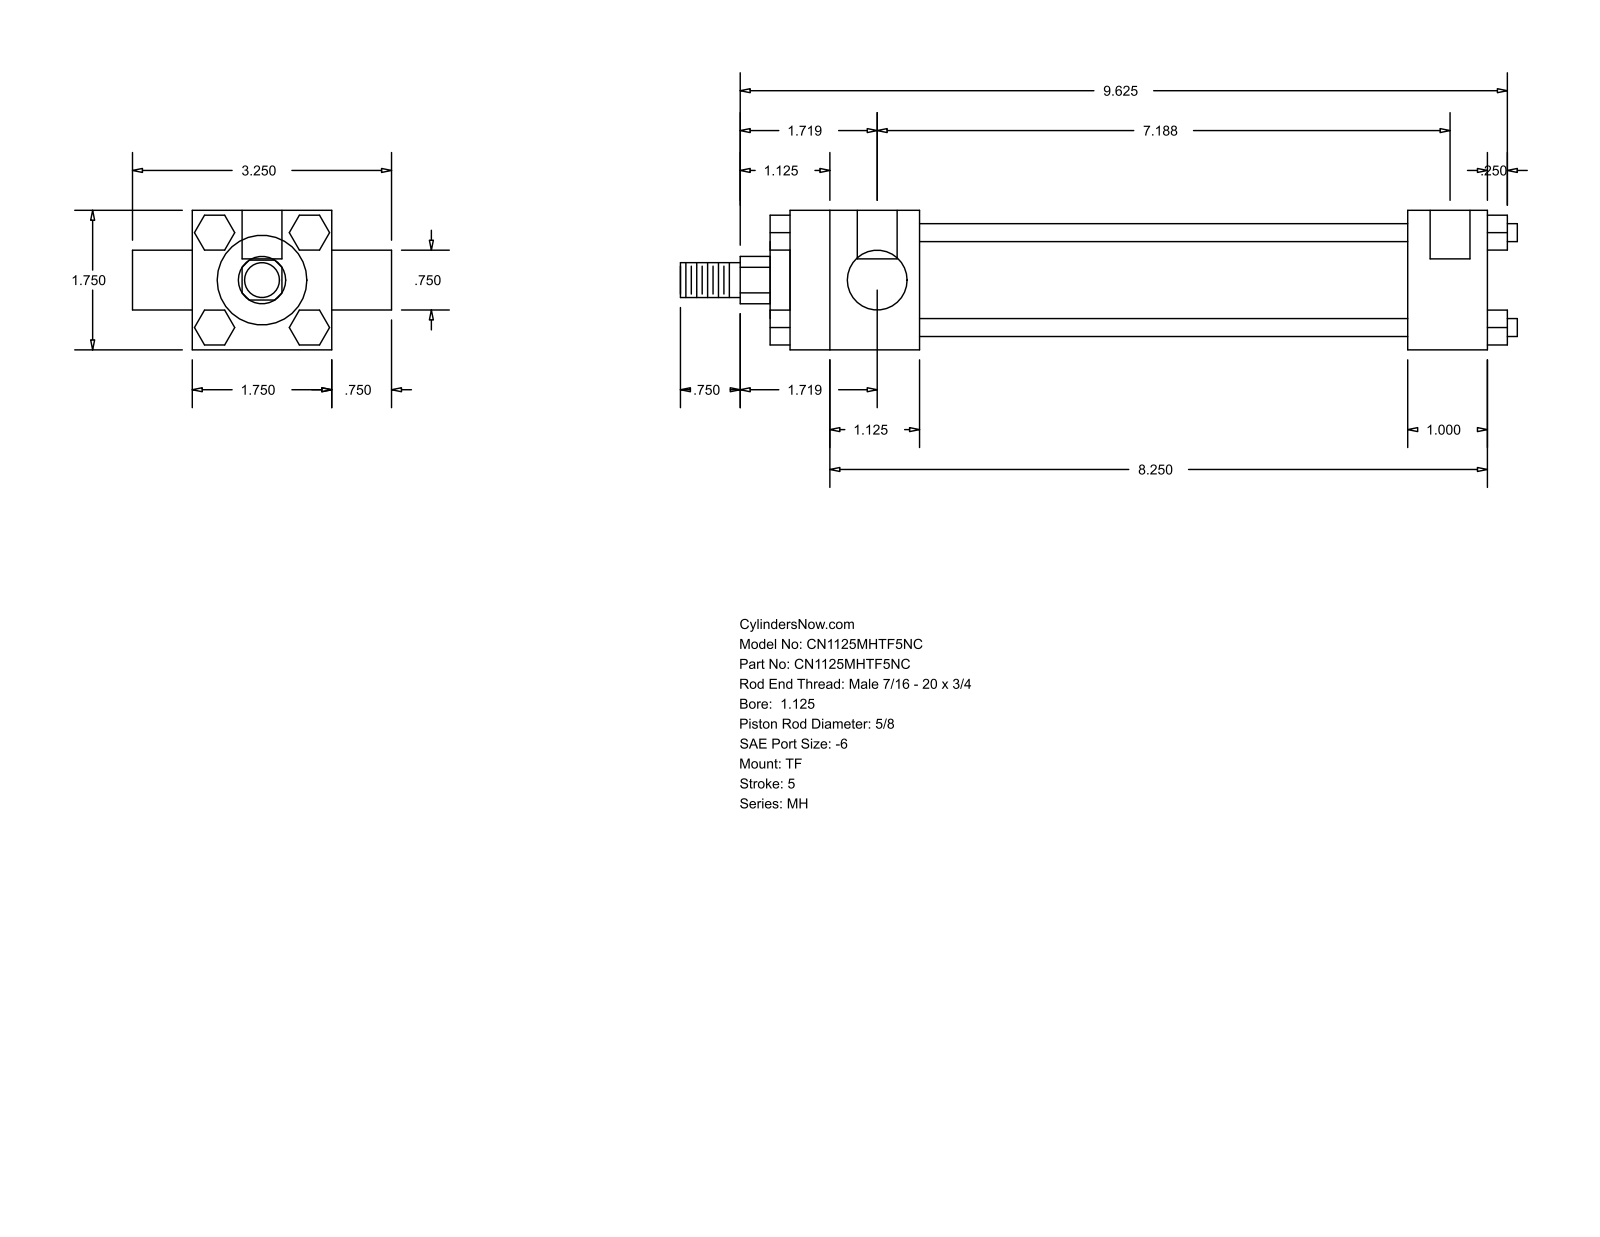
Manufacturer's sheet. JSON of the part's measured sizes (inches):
{"part_name": "MH_TF__0112_0.625", "step_written_by": "GSSL Pune (CONFIG_CONTROL_DESIGN)", "units": "inches", "bodies": {"solids": 0, "faces": 120, "planar": 92, "cylindrical": 28, "other": 0}, "overall_size": [10.5, 3.25, 1.75], "round_holes": [[0.219, 3], [0.5, 2]], "round_bosses_or_shafts": [[0.225, 4], [1.375, 1], [1.125, 1], [0.75, 1], [0.625, 1], [0.437, 1]], "partial_cylinders_radius": [[0.297, 1]], "face_to_face_distances": [1.75, 0.25, 9, 0.437, 1, 6.125, 7.125, 1.625, 7.75, 8.75], "hole_center_spacings": [0.125, 7.063, 7.187]}
